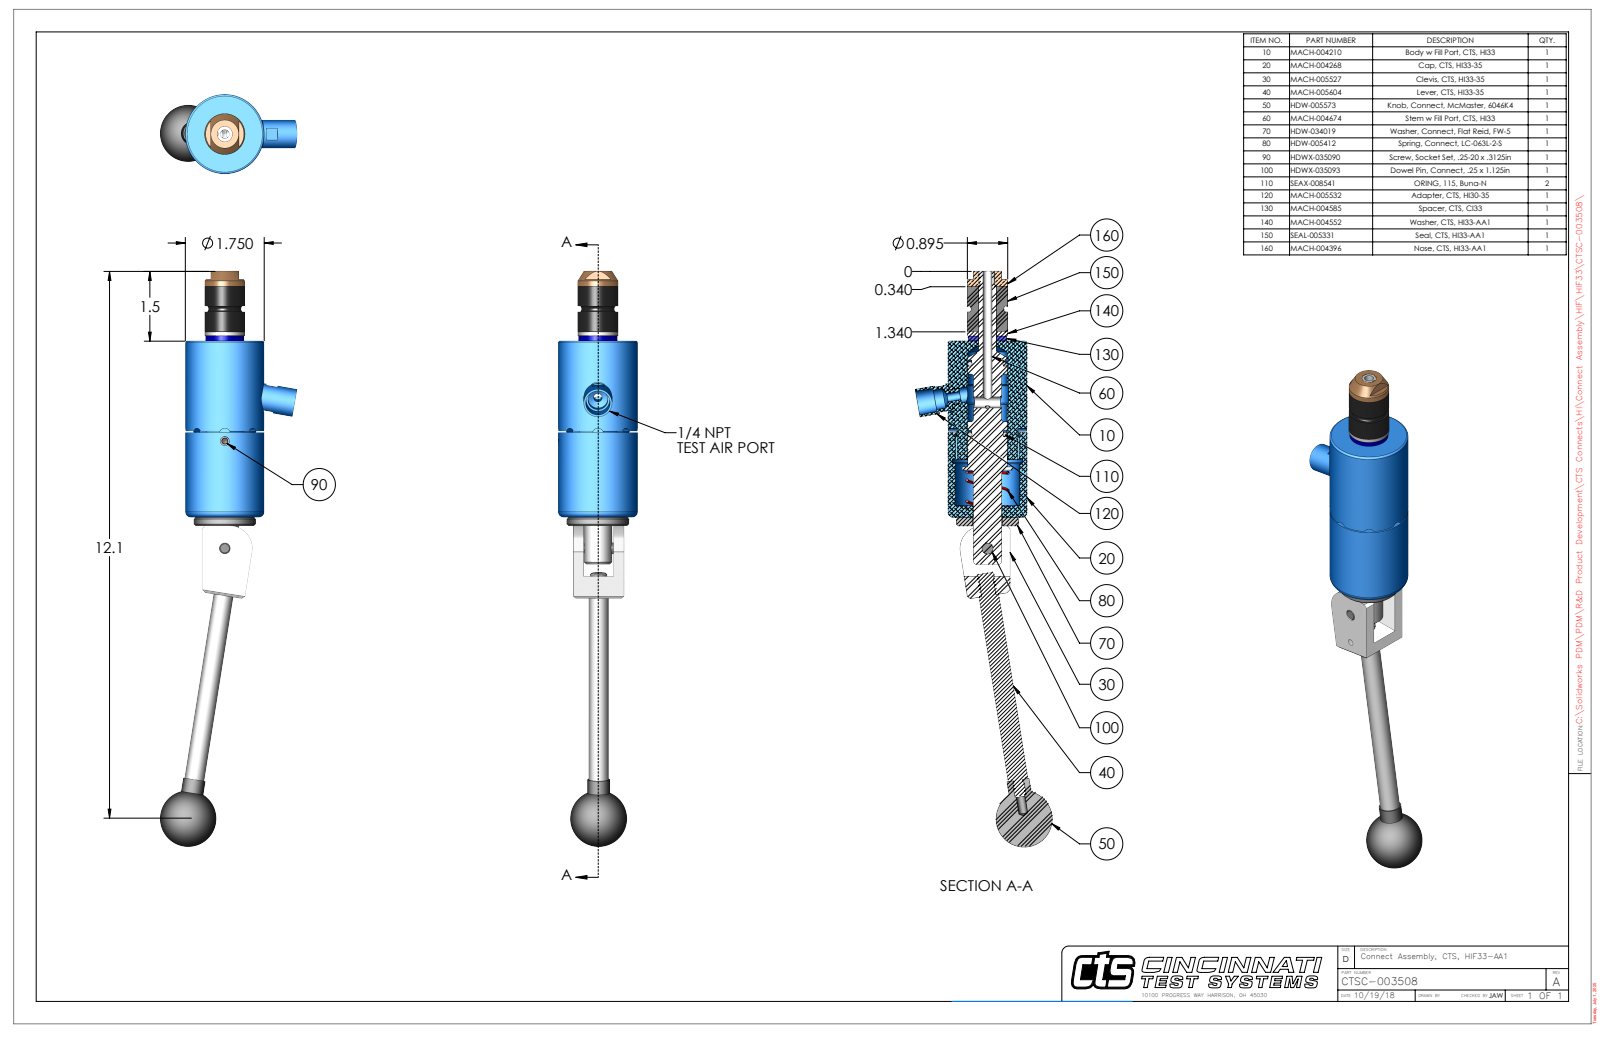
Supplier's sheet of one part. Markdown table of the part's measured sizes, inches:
| quantity | value |
| --- | --- |
| part name | CTSC-003508 |
| STEP written by | SolidWorks 2023 (AUTOMOTIVE_DESIGN) |
| units | inches |
| bodies | 10 solids, 277 faces (91 planar, 121 cylindrical, 65 other) |
| overall size | 12.751 × 3.043 × 1.75 |
| volume | 13.46 in³ |
| surface area | 74.45 in² |
| round holes (diameter × count) | 0.201 × 2, 0.313 × 2, 0.15 × 1, 0.187 × 1, 0.204 × 1, 0.249 × 1, 0.25 × 1, 0.251 × 1, 0.39 × 1, 0.397 × 1, 0.403 × 1, 0.438 × 1 |
| round bosses / shafts (diameter × count) | 0.375 × 2, 0.312 × 2, 0.25 × 2, 1.75 × 1, 1.38 × 1, 0.895 × 1, 0.895 × 1, 0.858 × 1 |
| partial cylindrical surfaces (radius × count) | 0.125 × 4, 0.029 × 2, 0.146 × 1, 0.33 × 1, 0.5 × 1, 0.695 × 1, 0.832 × 1 |
| main face-to-face distances | 3.907, 1.12, 0.188, 4.095, 0.888, 0.232, 0.232, 0.656, 0.888, 1.207 |
| hole center spacings | 0.74, 2.376, 3.116 |
